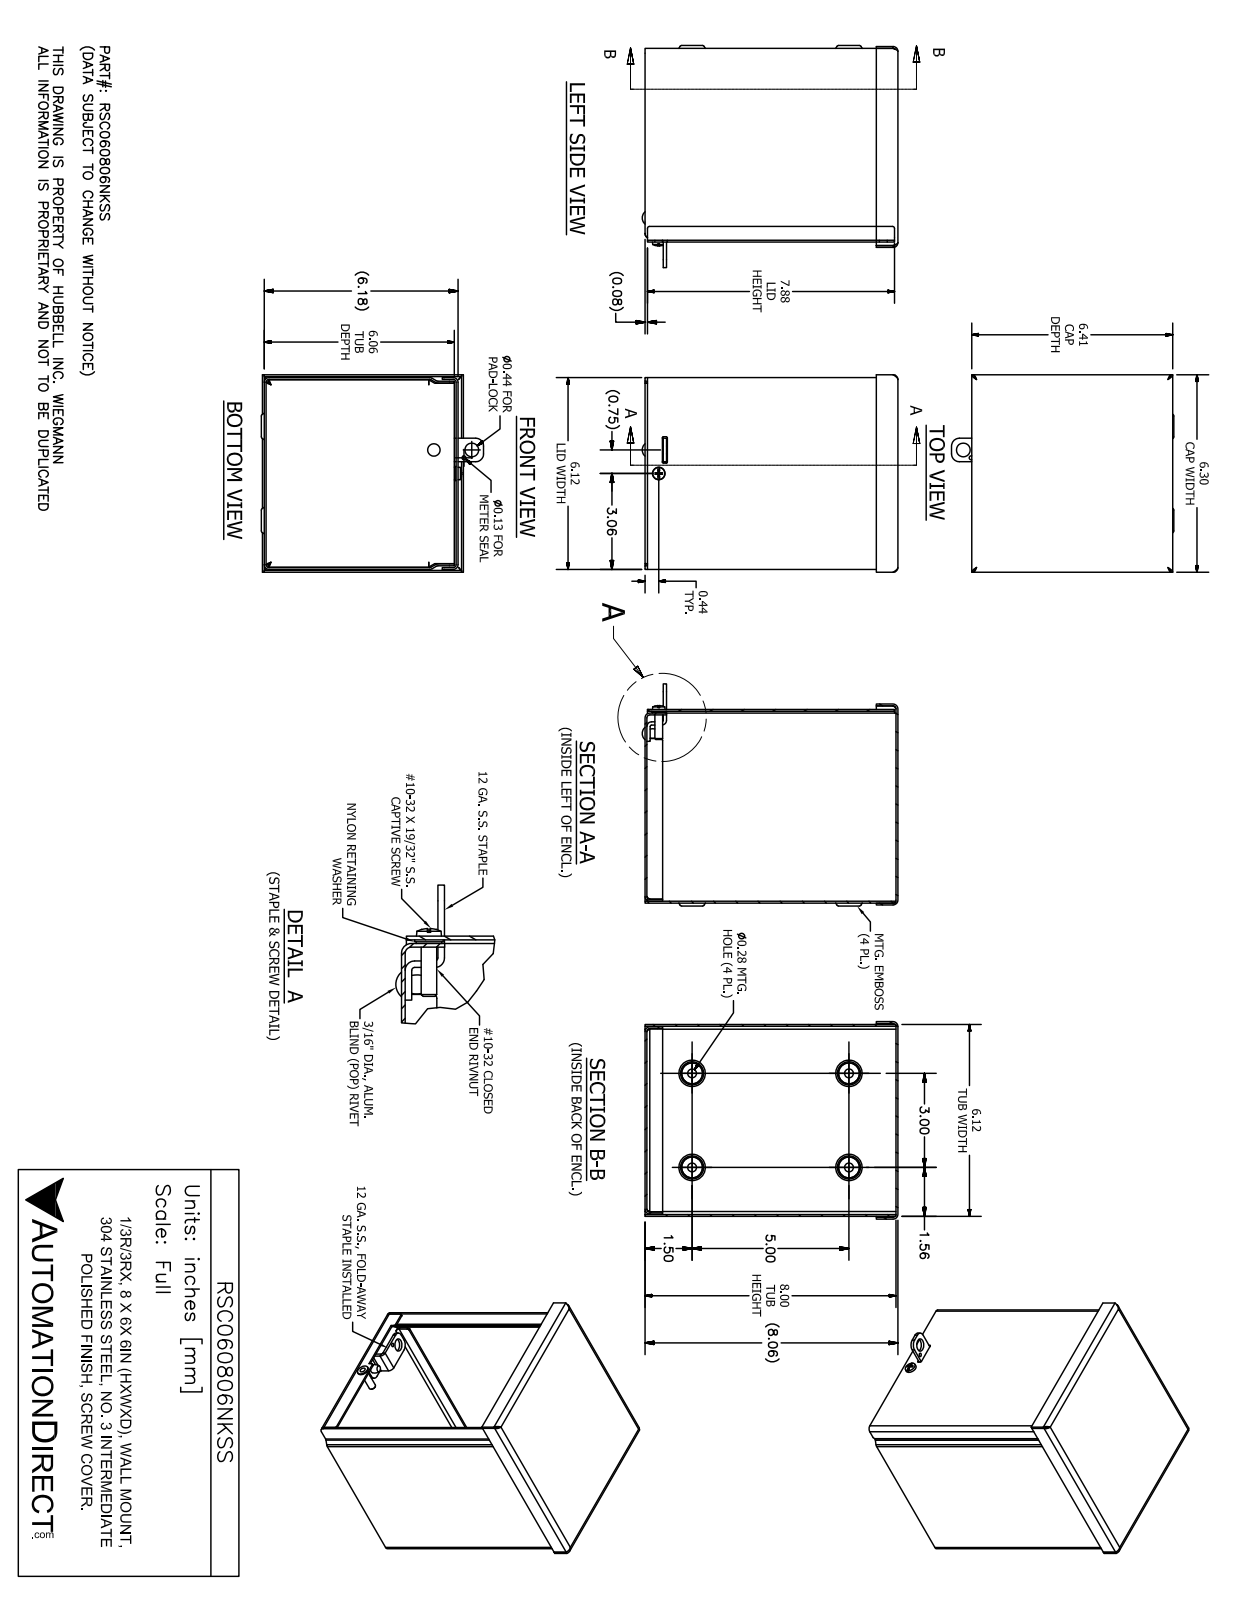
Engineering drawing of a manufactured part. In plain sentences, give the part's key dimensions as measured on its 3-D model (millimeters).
The part is named "RSC060806NKSS". Its 3-D file was written by "SolidWorks 2017 (AUTOMOTIVE_DESIGN)". It is 9 solids with 292 faces: 149 planar, 79 cylindrical and 64 other. Overall it measures 207 by 179.9 by 160 millimeters. Its volume is 293 300 cubic millimeters and its surface area 396 300 square millimeters. Round holes: 4 of diameter 7.1, 2 of diameter 6.4, 1 of diameter 3.2, 1 of diameter 4, 1 of diameter 5, 1 of diameter 5, 1 of diameter 5.1, 1 of diameter 6.5, 1 of diameter 7.1, 1 of diameter 11.1. Round bosses or shafts: 1 of diameter 11.5, 1 of diameter 10.3, 1 of diameter 6.3, 1 of diameter 4.7, 1 of diameter 4.2. Partial cylindrical surfaces (rounded edges, fillets, slot ends): 16 of radius 2.4, 16 of radius 3.9, 6 of radius 0.8, 4 of radius 6.4, 3 of radius 1.6, 2 of radius 1.2, 2 of radius 1.3, 2 of radius 1.6. The main face-to-face distances are 1.5, 153.9, 155.4, 203.2, 152.4, 156.9, 155.4, 153.9, 204.7, 201.7. The hole center spacings are 46.7, 47.1, 76.2, 127, 148.1, 158.6, 159.4, 9.
